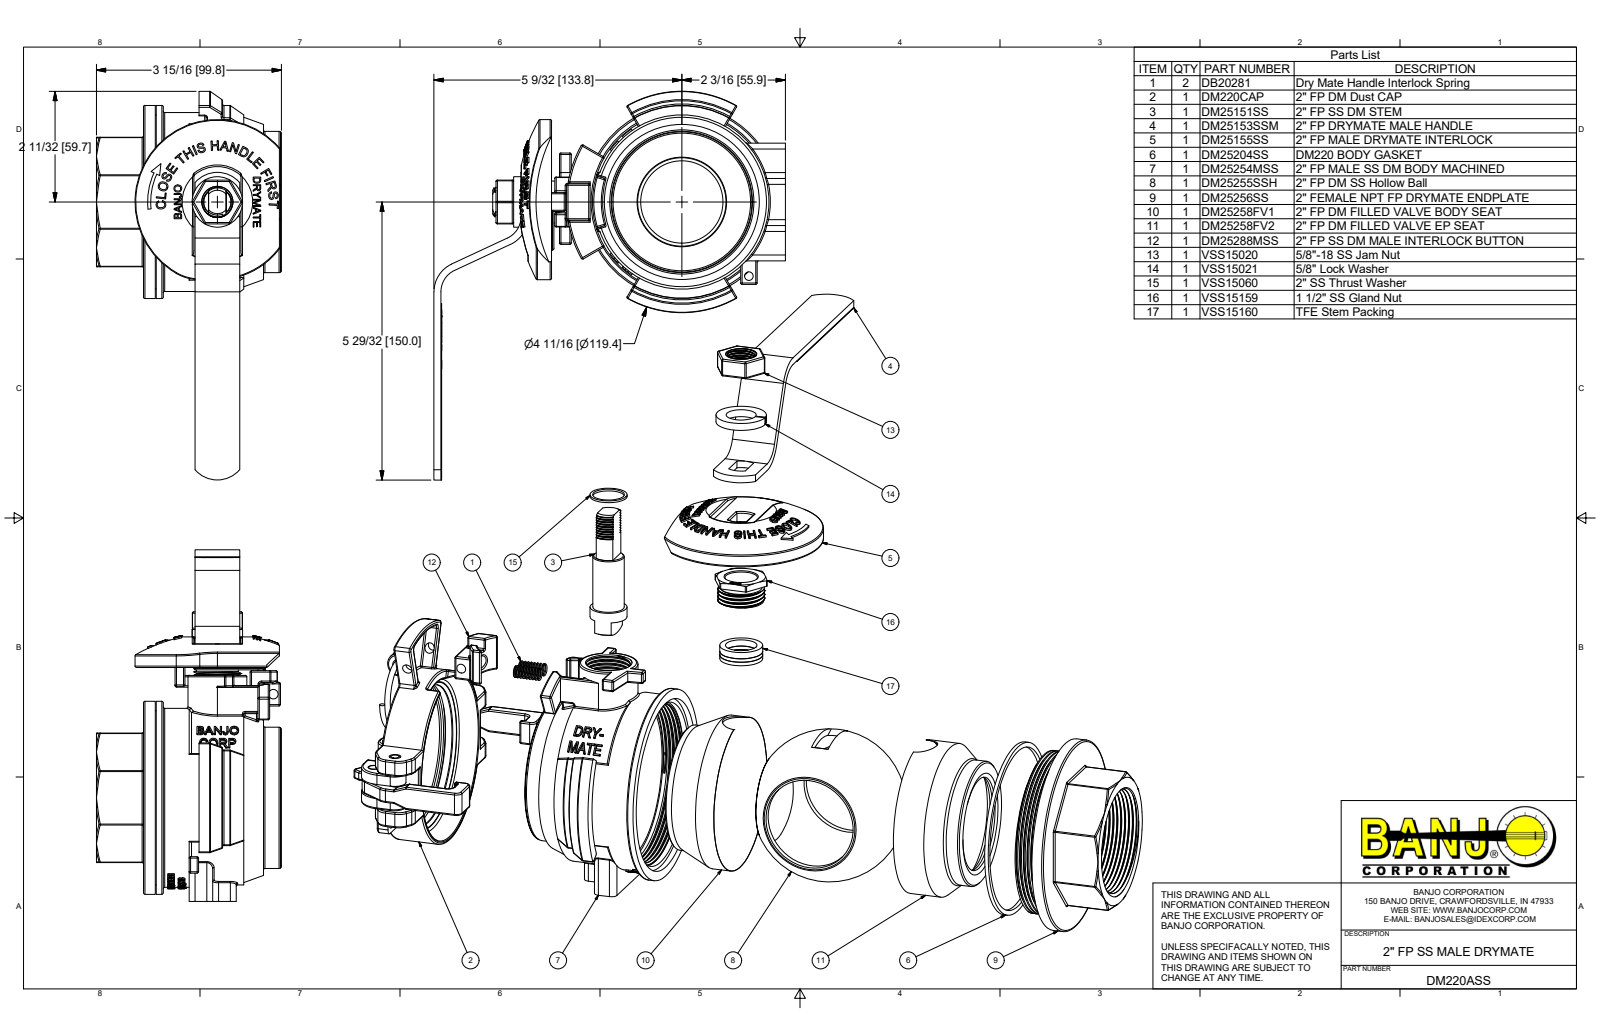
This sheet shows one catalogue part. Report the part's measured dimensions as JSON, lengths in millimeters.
{"part_name": "DM220ASS; DM220ASSX; DM25254MSS; DB20281 (+8 more)", "step_written_by": "Autodesk Inventor 2017 (AUTOMOTIVE_DESIGN)", "units": "millimeters", "bodies": {"solids": 22, "faces": 2463, "planar": 857, "cylindrical": 472, "other": 1134}, "overall_size": [209.68, 189.7, 99.82], "volume_mm3": 417502, "surface_area_mm2": 219511, "round_holes": [[4.57, 1], [5.08, 1], [14.73, 1], [16.26, 1], [16.82, 1], [17.02, 1], [17.17, 1], [17.53, 1], [21.34, 1], [22.26, 1], [23.37, 1], [25.4, 1]], "round_bosses_or_shafts": [[104.14, 1], [96.52, 1], [93.98, 1], [93.8, 1], [88.65, 1], [86.33, 1], [83.57, 1], [76.2, 1]], "partial_cylinders_radius": [[0.76, 222], [3.17, 8], [16.51, 3], [1.52, 2], [3.43, 2], [10.16, 2], [12.7, 2], [15.88, 2]], "face_to_face_distances": [3.81, 4.07, 12.7, 63.5, 69.84, 70.35, 74.42, 6.35, 46.99, 2.79], "hole_center_spacings": [53.95, 63.54]}
